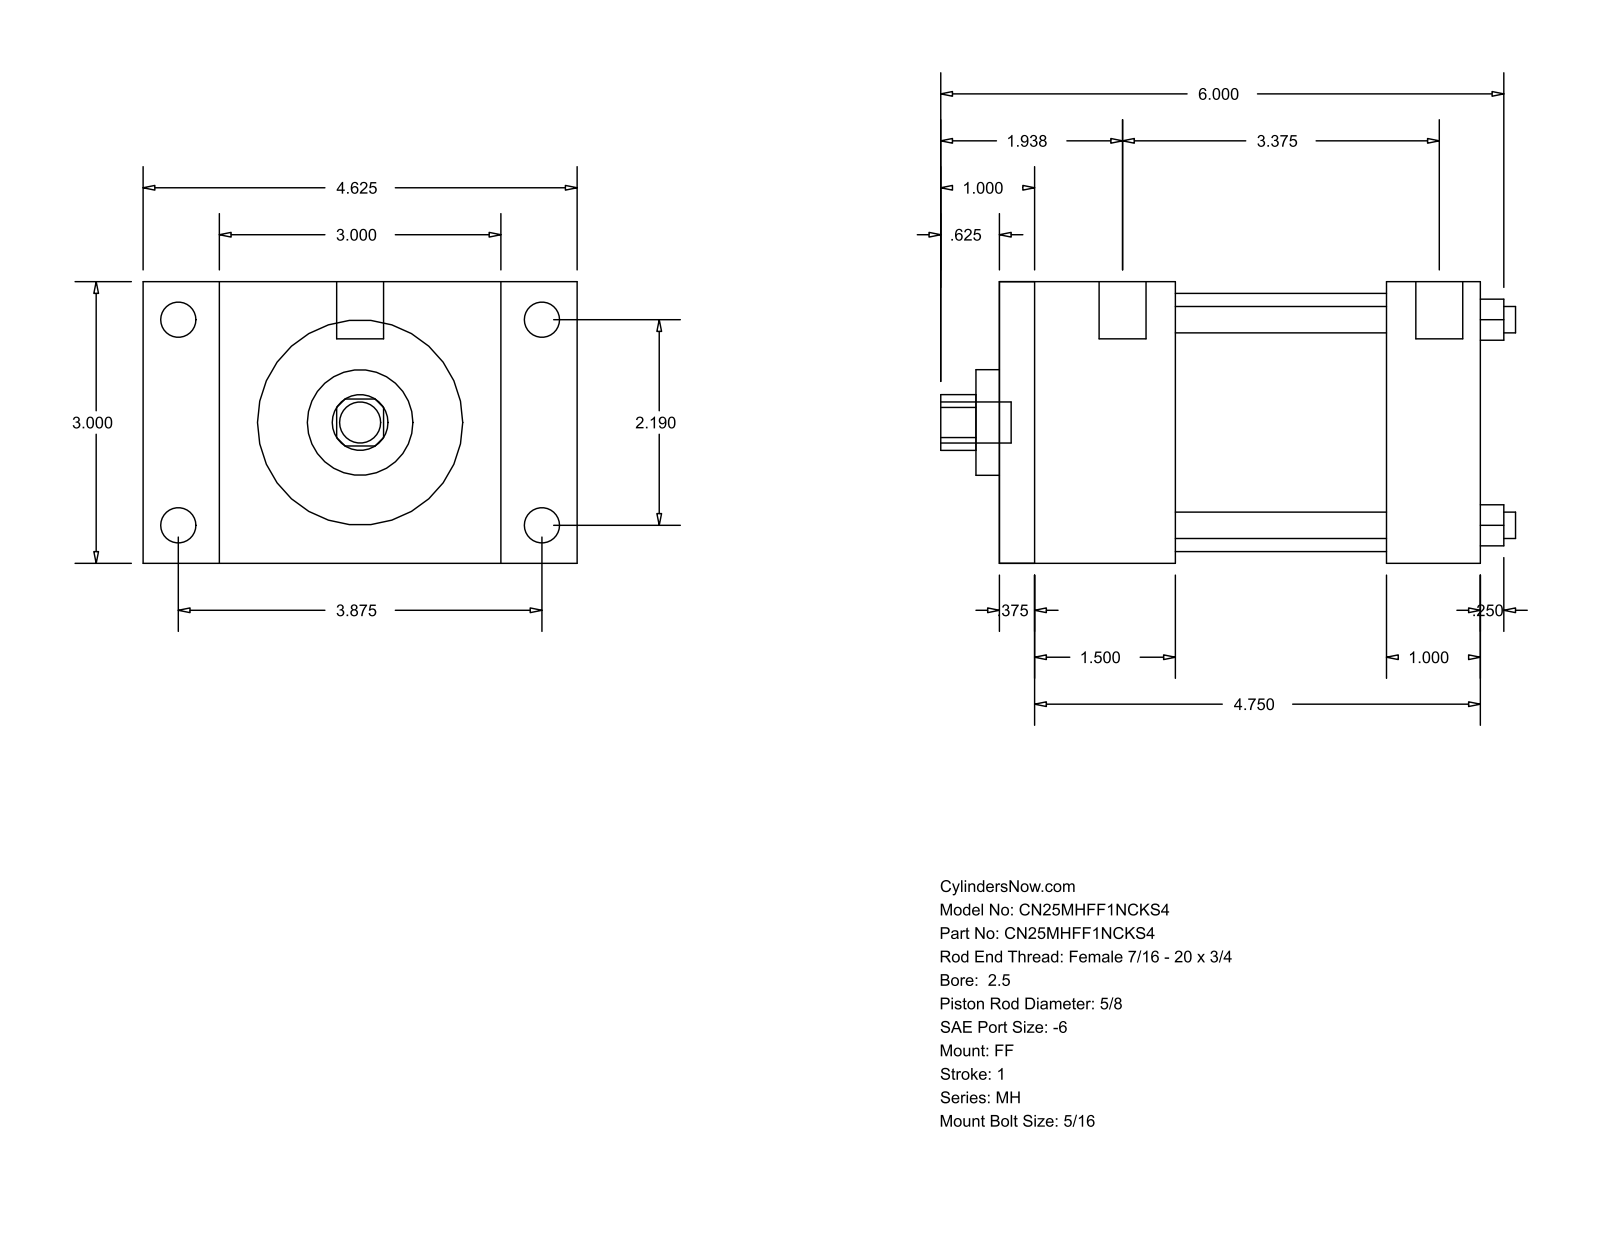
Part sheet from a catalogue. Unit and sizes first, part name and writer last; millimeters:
Units: millimetres
Overall size (bounding box): 155.57 × 117.47 × 76.2
Round holes (diameter × count): ⌀7.14 ×4, ⌀15.88 ×1, ⌀28.57 ×1, ⌀69.85 ×1
Round bosses / shafts (diameter × count): ⌀9.53 ×4, ⌀5.56 ×4, ⌀12.7 ×2, ⌀11.11 ×1
Partial cylindrical surfaces — rounded edges, fillets, slot ends (radius × count): R7.54 ×1
Main face-to-face distances: 76.2, 130.17, 9.52, 120.65, 25.4, 57.15, 47.62, 104.77, 38.1, 95.25
Hole centre spacings: 39.33, 55.62, 78.66
Bodies: 0 solids, 92 faces (64 planar, 28 cylindrical, 0 other)
Part name (STEP PRODUCT): MH_FF__0250_0.625
STEP written by: GSSL Pune (CONFIG_CONTROL_DESIGN)
